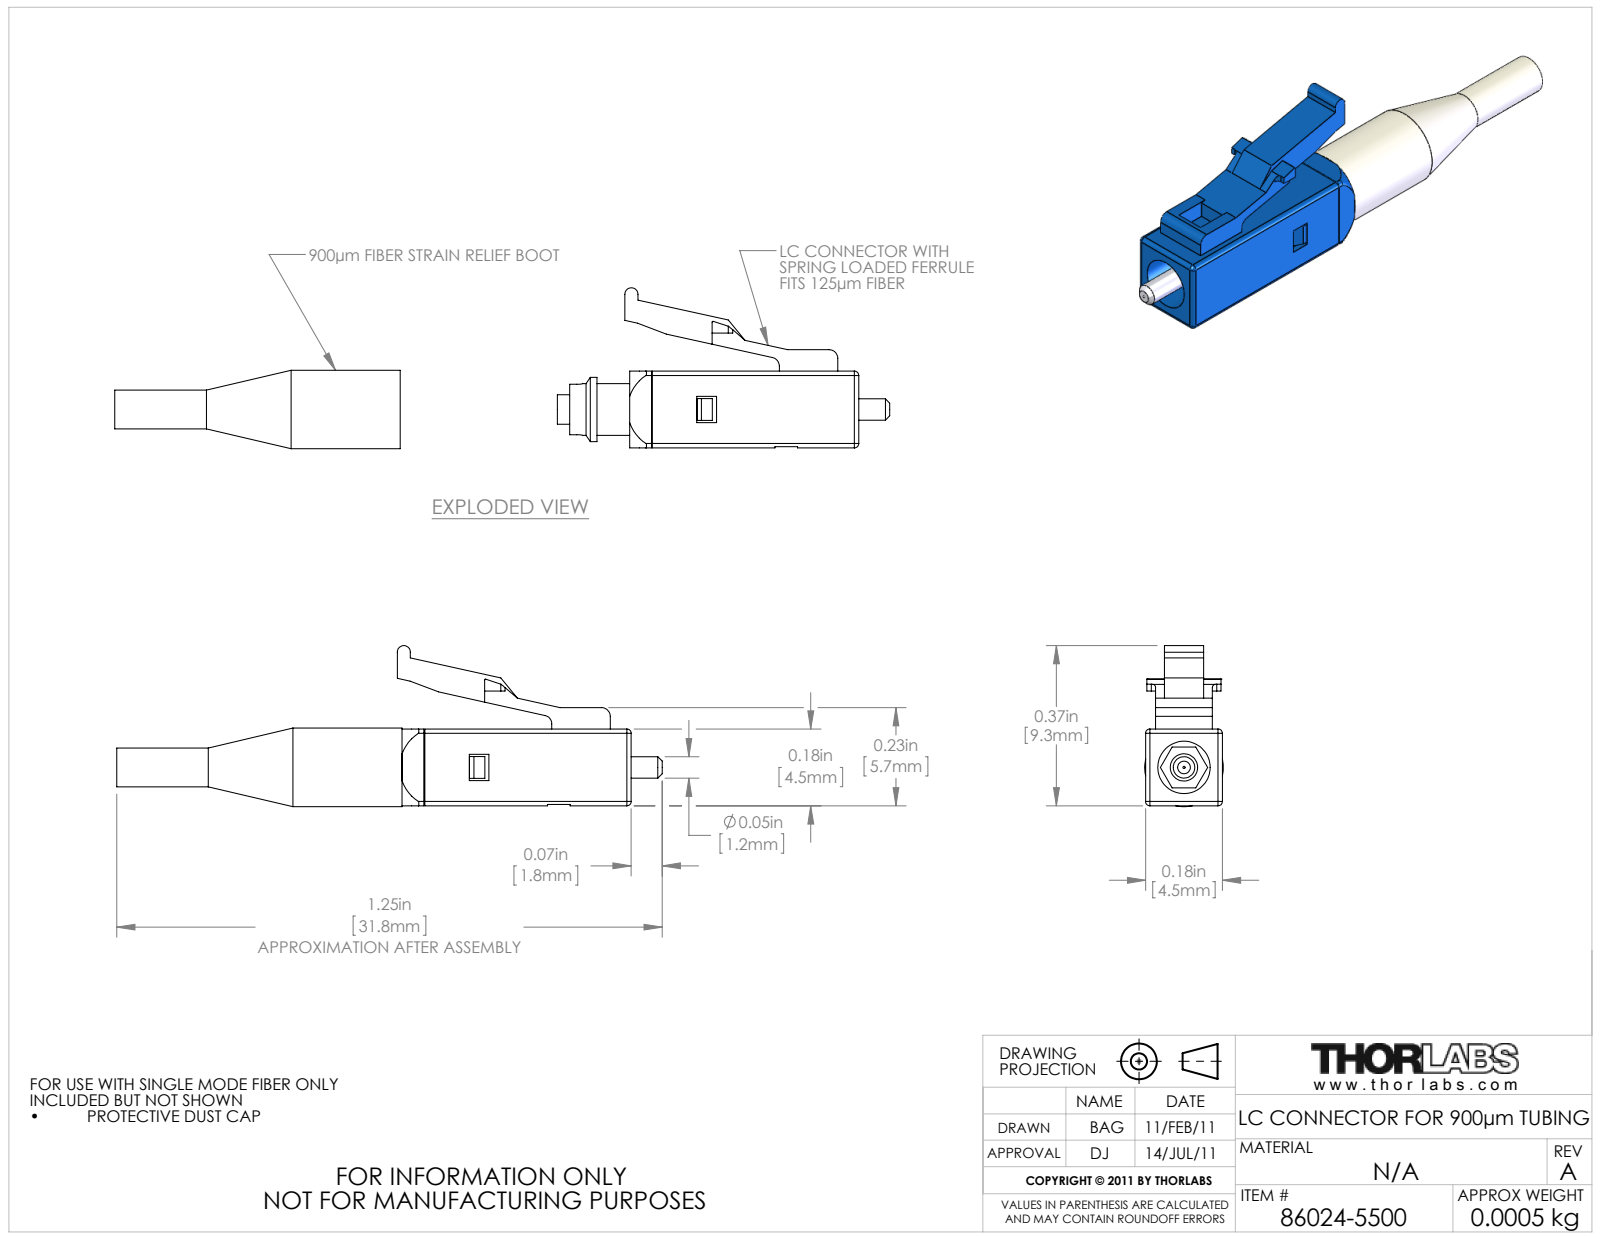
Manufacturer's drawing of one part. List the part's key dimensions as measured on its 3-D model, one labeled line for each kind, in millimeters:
Part name (STEP PRODUCT): 5294-E0W
STEP written by: SolidWorks 2011 (AUTOMOTIVE_DESIGN)
Units: millimetres
Bodies: 2 solids, 167 faces (97 planar, 54 cylindrical, 16 other)
Overall size (bounding box): 31.8 × 9.4 × 4.6
Volume: 430 mm³ · Surface area: 873 mm²
Round holes (diameter × count): ⌀1 ×1, ⌀1.1 ×1, ⌀1.6 ×1, ⌀1.7 ×1, ⌀2.4 ×1, ⌀2.4 ×1, ⌀3 ×1, ⌀3.2 ×1
Round bosses / shafts (diameter × count): ⌀4.6 ×1, ⌀3.7 ×1, ⌀3 ×1, ⌀2.3 ×1, ⌀1.7 ×1, ⌀1.2 ×1
Partial cylindrical surfaces — rounded edges, fillets, slot ends (radius × count): R0.3 ×10, R0.5 ×2, R0.4 ×1, R0.4 ×1
Main face-to-face distances: 4.5, 0.5, 1.1, 3.4, 2.8, 1.6, 0.6, 3.9, 1.3, 0.6
